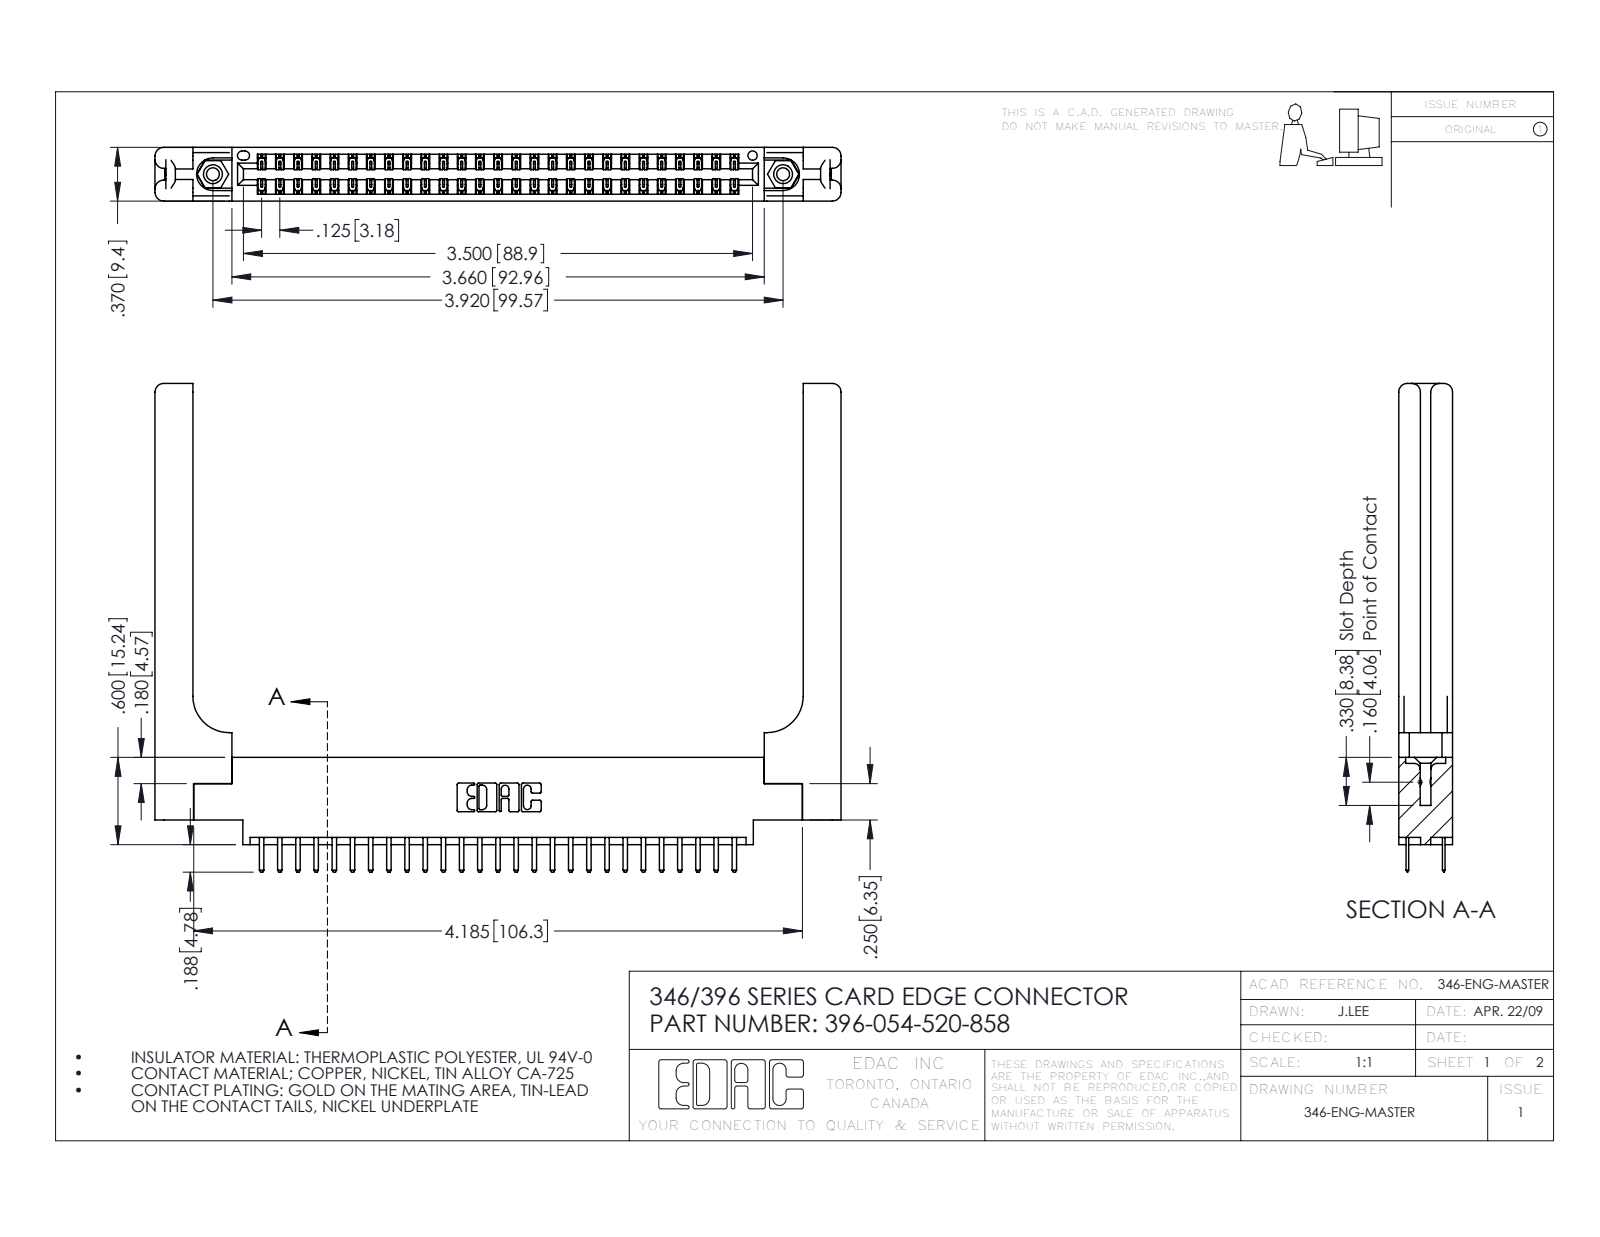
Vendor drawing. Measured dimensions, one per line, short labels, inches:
name: 346 Part_0.170 Offset - 0.156 Dia-TH; 396-054-520-858; 346-220-058_345-220-058; 345-250-001_345-250-001-102 (+1 more)
written by: SolidWorks 2016 (CONFIG_CONTROL_DESIGN)
unit: in
bodies: 59 solids, 3406 faces (2226 planar, 1120 cylindrical, 60 other)
size: 4.716 × 3.358 × 0.37
volume: 1.152 in³; area: 31.79 in²
holes: 2× ⌀0.089, 2× ⌀0.125, 2× ⌀0.156, 1× ⌀0.064
bosses: 2× ⌀0.155
rounds: 81× R0.006, 58× R0.01, 22× R0.01, 16× R0.06, 6× R0.007, 6× R0.031, 3× R0.026, 2× R0.014
face distances: 0.37, 0.072, 0.048, 0.322, 0.148, 0.15, 0.25, 0.298, 0.025, 0.275
hole spacings: 0.246, 3.712, 3.92
